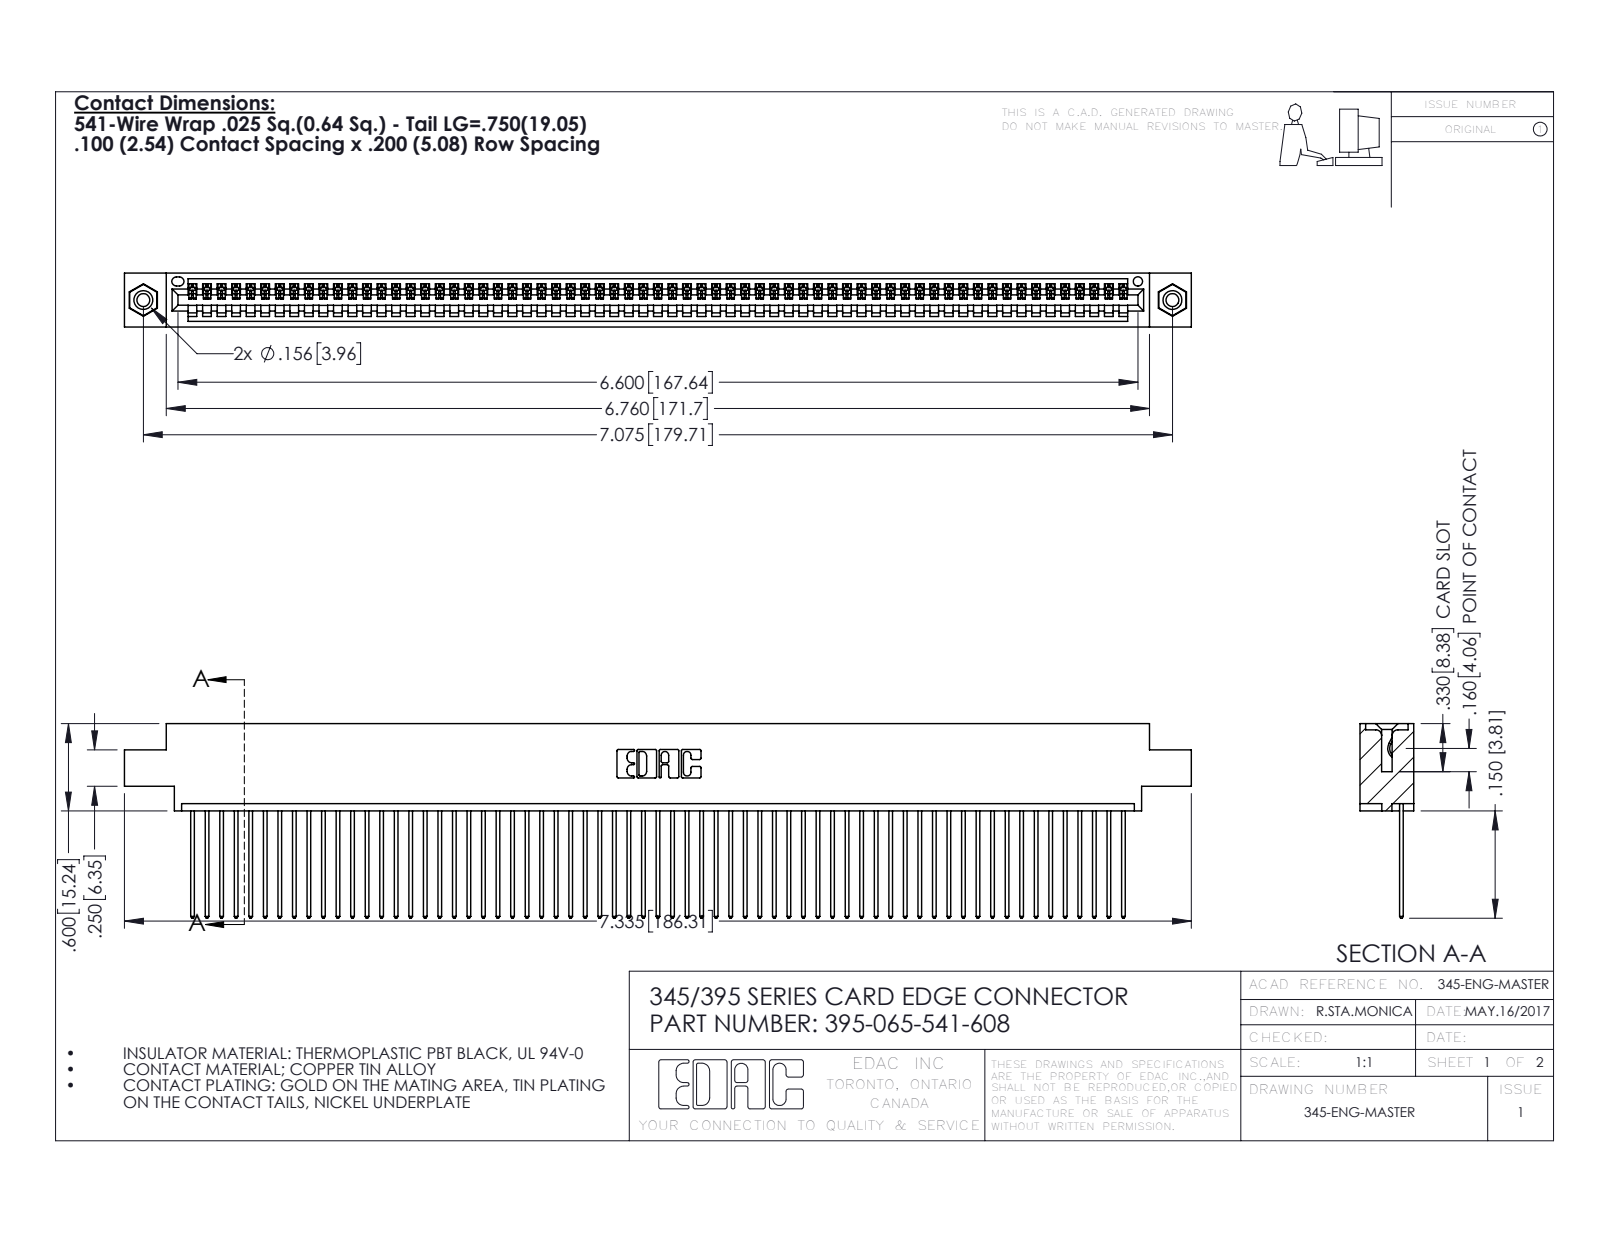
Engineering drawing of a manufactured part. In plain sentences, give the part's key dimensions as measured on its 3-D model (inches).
The part is named "345-250-001_345-250-003-102; 345-292-001_345-293-141; 395-065-541-608; 345 Part_0.170 Offset - 0.156 Dia-TI". Its 3-D file was written by "SolidWorks 2016 (CONFIG_CONTROL_DESIGN)". It is 68 solids with 3960 faces: 2716 planar, 1228 cylindrical and 16 other. Overall it measures 7.335 by 1.337 by 0.37 inches. Its volume is 1.097 cubic inches and its surface area 39.7 square inches. Round holes: 2 of diameter 0.089, 2 of diameter 0.125, 2 of diameter 0.156, 1 of diameter 0.064. Round bosses or shafts: 2 of diameter 0.155. Partial cylindrical surfaces (rounded edges, fillets, slot ends): 130 of radius 0.006, 130 of radius 0.01, 22 of radius 0.01, 6 of radius 0.007, 6 of radius 0.031, 3 of radius 0.026, 2 of radius 0.031, 2 of radius 0.04. The main face-to-face distances are 0.072, 0.298, 0.098, 0.272, 0.025, 0.37, 0.2, 0.225, 0.175, 0.149. The hole center spacings are 0.27, 6.839, 7.075.
